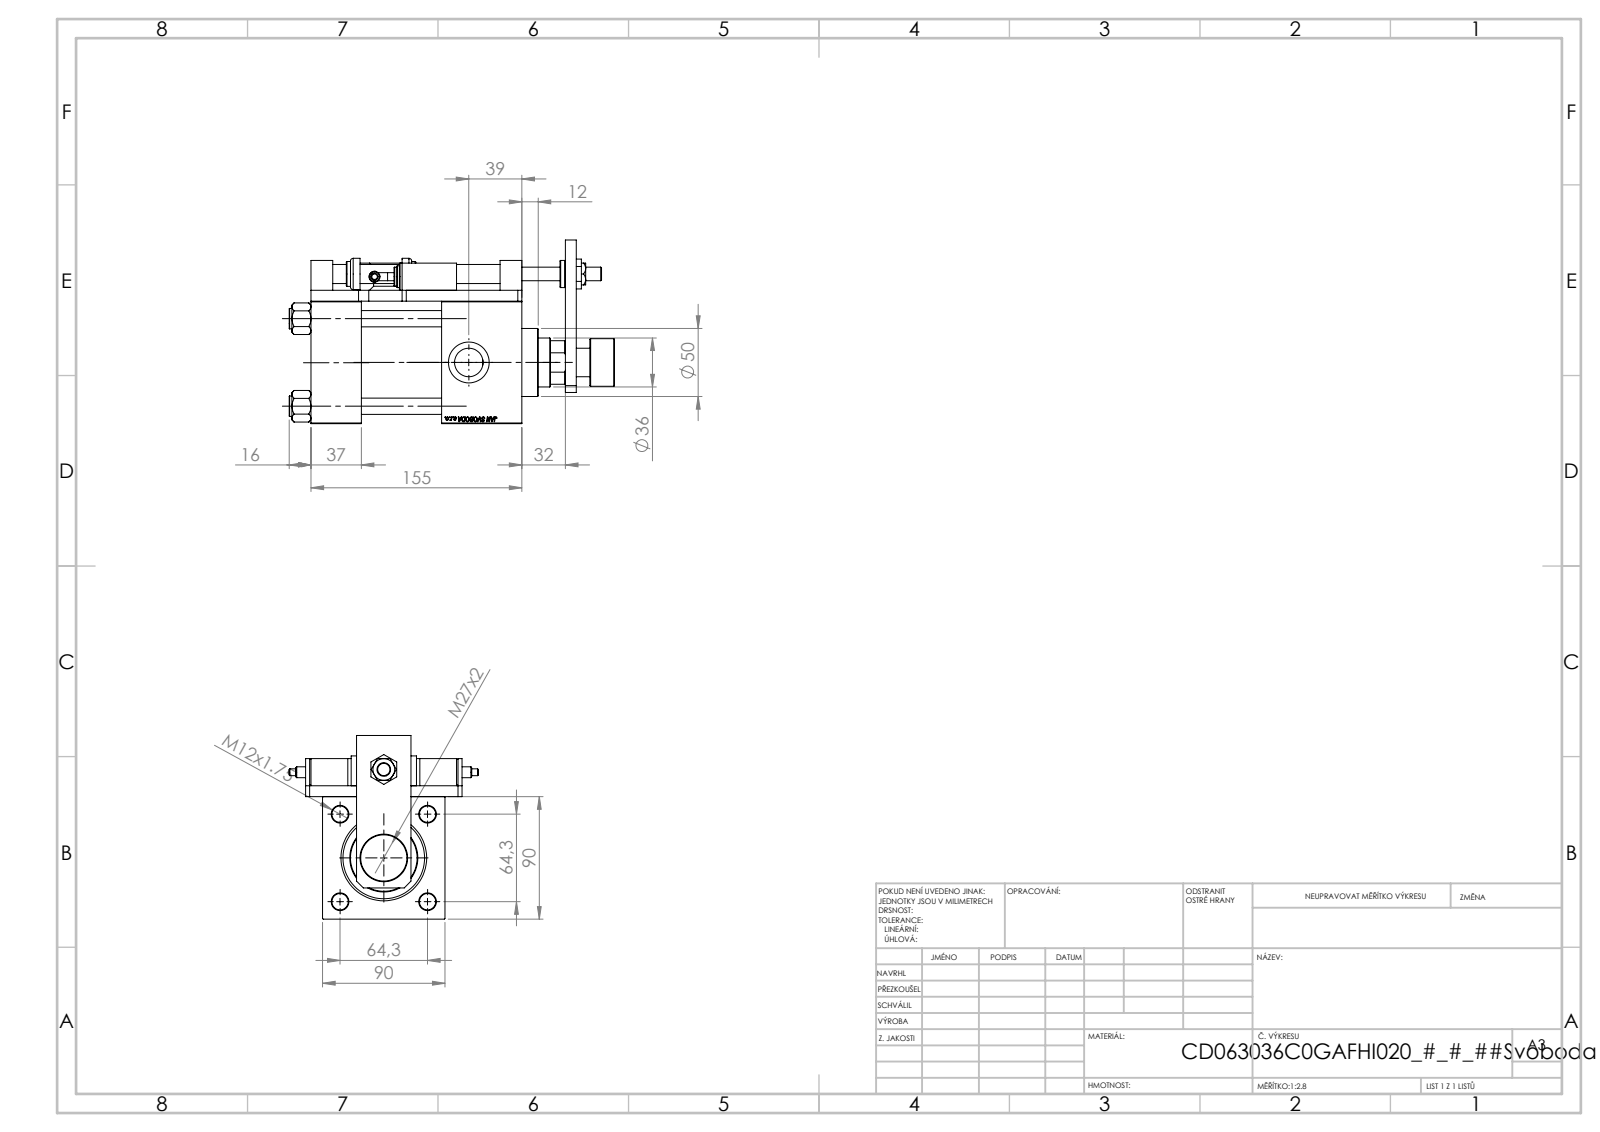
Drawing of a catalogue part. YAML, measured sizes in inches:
part_name: "NUT_M5_V215CD_C; V215CD_SWITCH_Q_ZARAZKA; V215CD_SWITCH_Q_BLOK; V215CD_SWITCH_Q_MAGNET (+7 more)"
step_written_by: "SolidWorks 2019 (CONFIG_CONTROL_DESIGN)"
units: inches
bodies: {solids: 25, faces: 1419, planar: 655, cylindrical: 167, other: 597}
overall_size: [9.409, 5.473, 5.315]
volume: 76.65
surface_area: 427.3
round_holes:
  - {diameter: 0.335, count: 4}
  - {diameter: 0.472, count: 4}
  - {diameter: 0.531, count: 4}
  - {diameter: 0.276, count: 2}
  - {diameter: 0.825, count: 2}
  - {diameter: 1.181, count: 2}
  - {diameter: 0.394, count: 1}
  - {diameter: 0.551, count: 1}
  - {diameter: 1.004, count: 1}
  - {diameter: 1.063, count: 1}
  - {diameter: 1.417, count: 1}
  - {diameter: 1.535, count: 1}
round_bosses_or_shafts:
  - {diameter: 0.591, count: 4}
  - {diameter: 0.787, count: 3}
  - {diameter: 0.63, count: 2}
  - {diameter: 0.551, count: 2}
  - {diameter: 0.315, count: 2}
  - {diameter: 0.236, count: 2}
  - {diameter: 0.198, count: 2}
  - {diameter: 2.717, count: 1}
partial_cylinders:
  - {radius: 0.295, count: 4}
face_to_face_distances: [0.315, 3.543, 1.457, 2.323, 4.646, 3.858, 6.102, 0.787, 1.26, 3.583]
hole_center_spacings: [1.79, 2.531, 0.754, 1.26, 1.809, 3.58, 4.029, 5.098]
